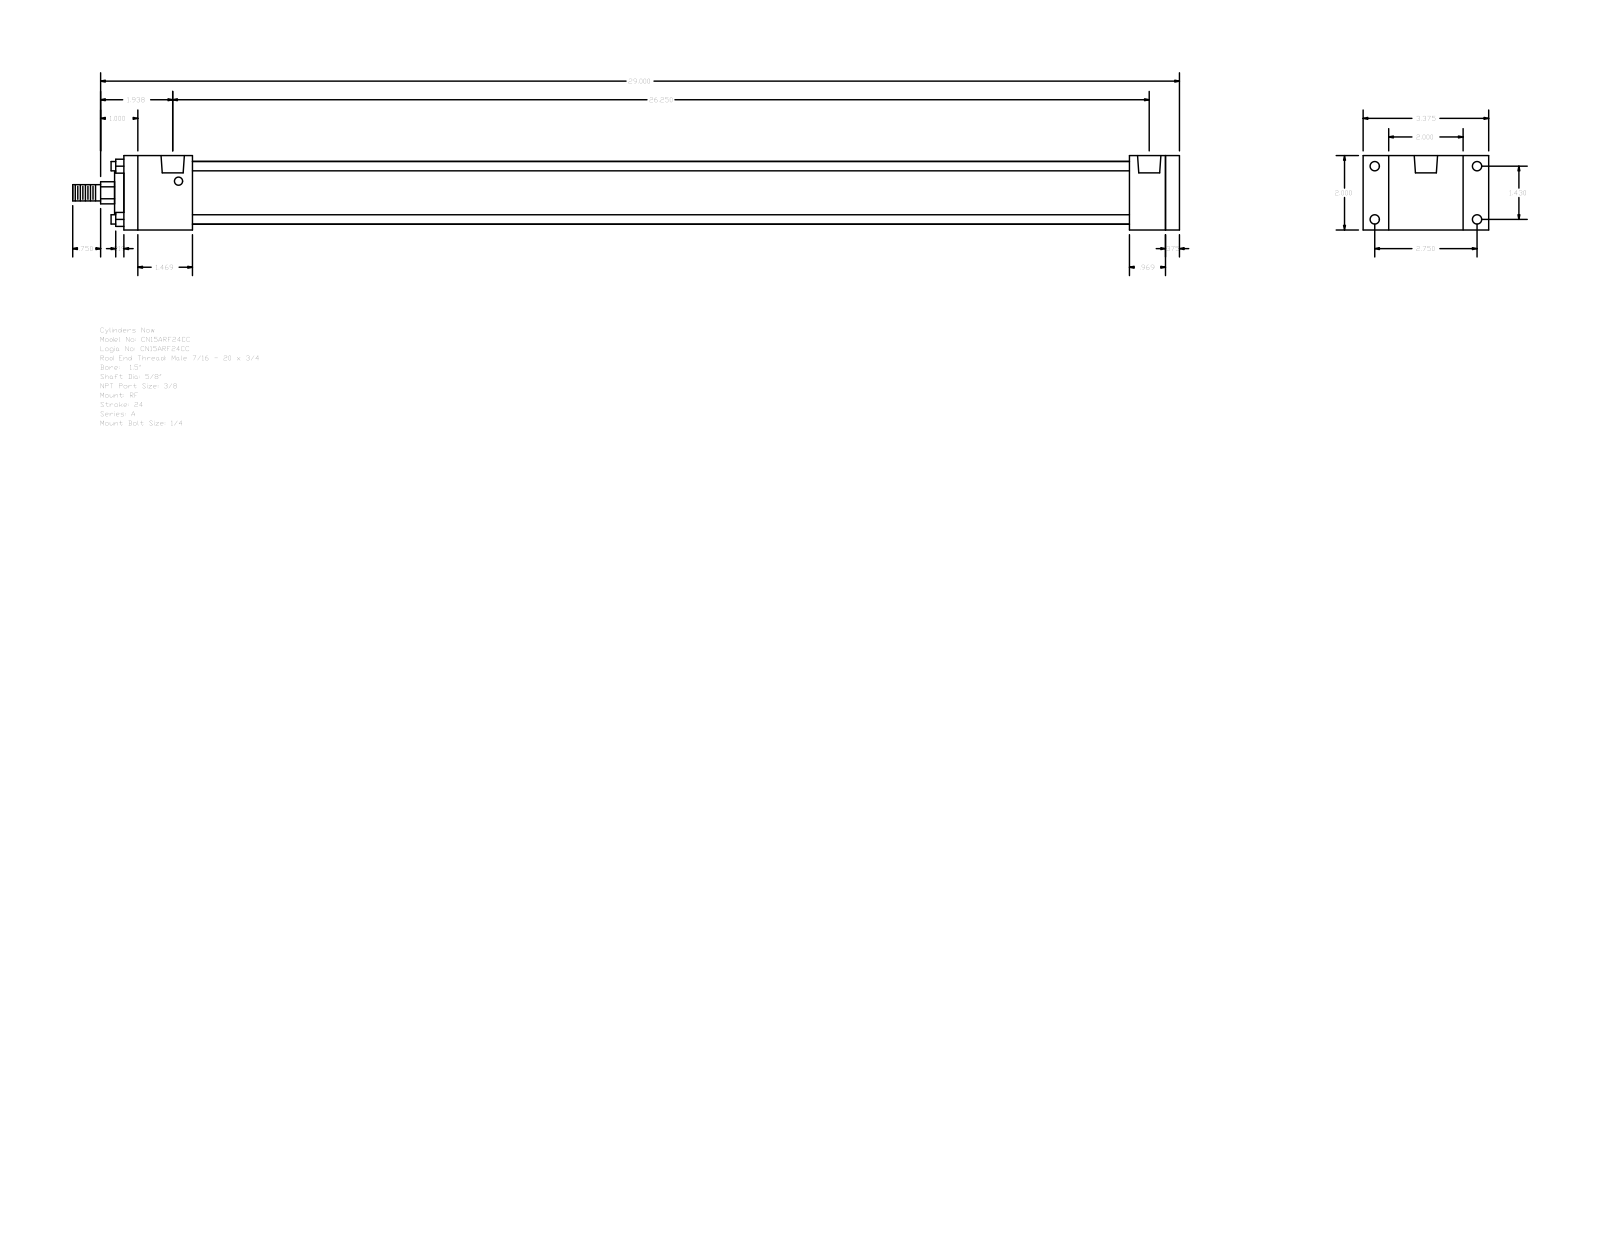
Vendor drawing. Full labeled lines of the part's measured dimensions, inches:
Part name (STEP PRODUCT): A_RF__0150_0.625
STEP written by: GSSL Pune (CONFIG_CONTROL_DESIGN)
Units: inches
Bodies: 0 solids, 92 faces (64 planar, 28 cylindrical, 0 other)
Overall size (bounding box): 29.75 × 3.375 × 2
Round holes (diameter × count): ⌀0.219 ×4, ⌀0.25 ×4, ⌀0.627 ×2
Round bosses / shafts (diameter × count): ⌀0.25 ×4, ⌀1.69 ×1, ⌀1.125 ×1, ⌀0.625 ×1, ⌀0.437 ×1
Partial cylindrical surfaces — rounded edges, fillets, slot ends (radius × count): R0.297 ×1
Main face-to-face distances: 2, 0.375, 28, 28.375, 27.031, 0.969, 1.344, 1.844, 25.187, 26.156
Hole centre spacings: 0.156, 1.43, 2.75, 3.099, 25.937, 26.094, 26.25
